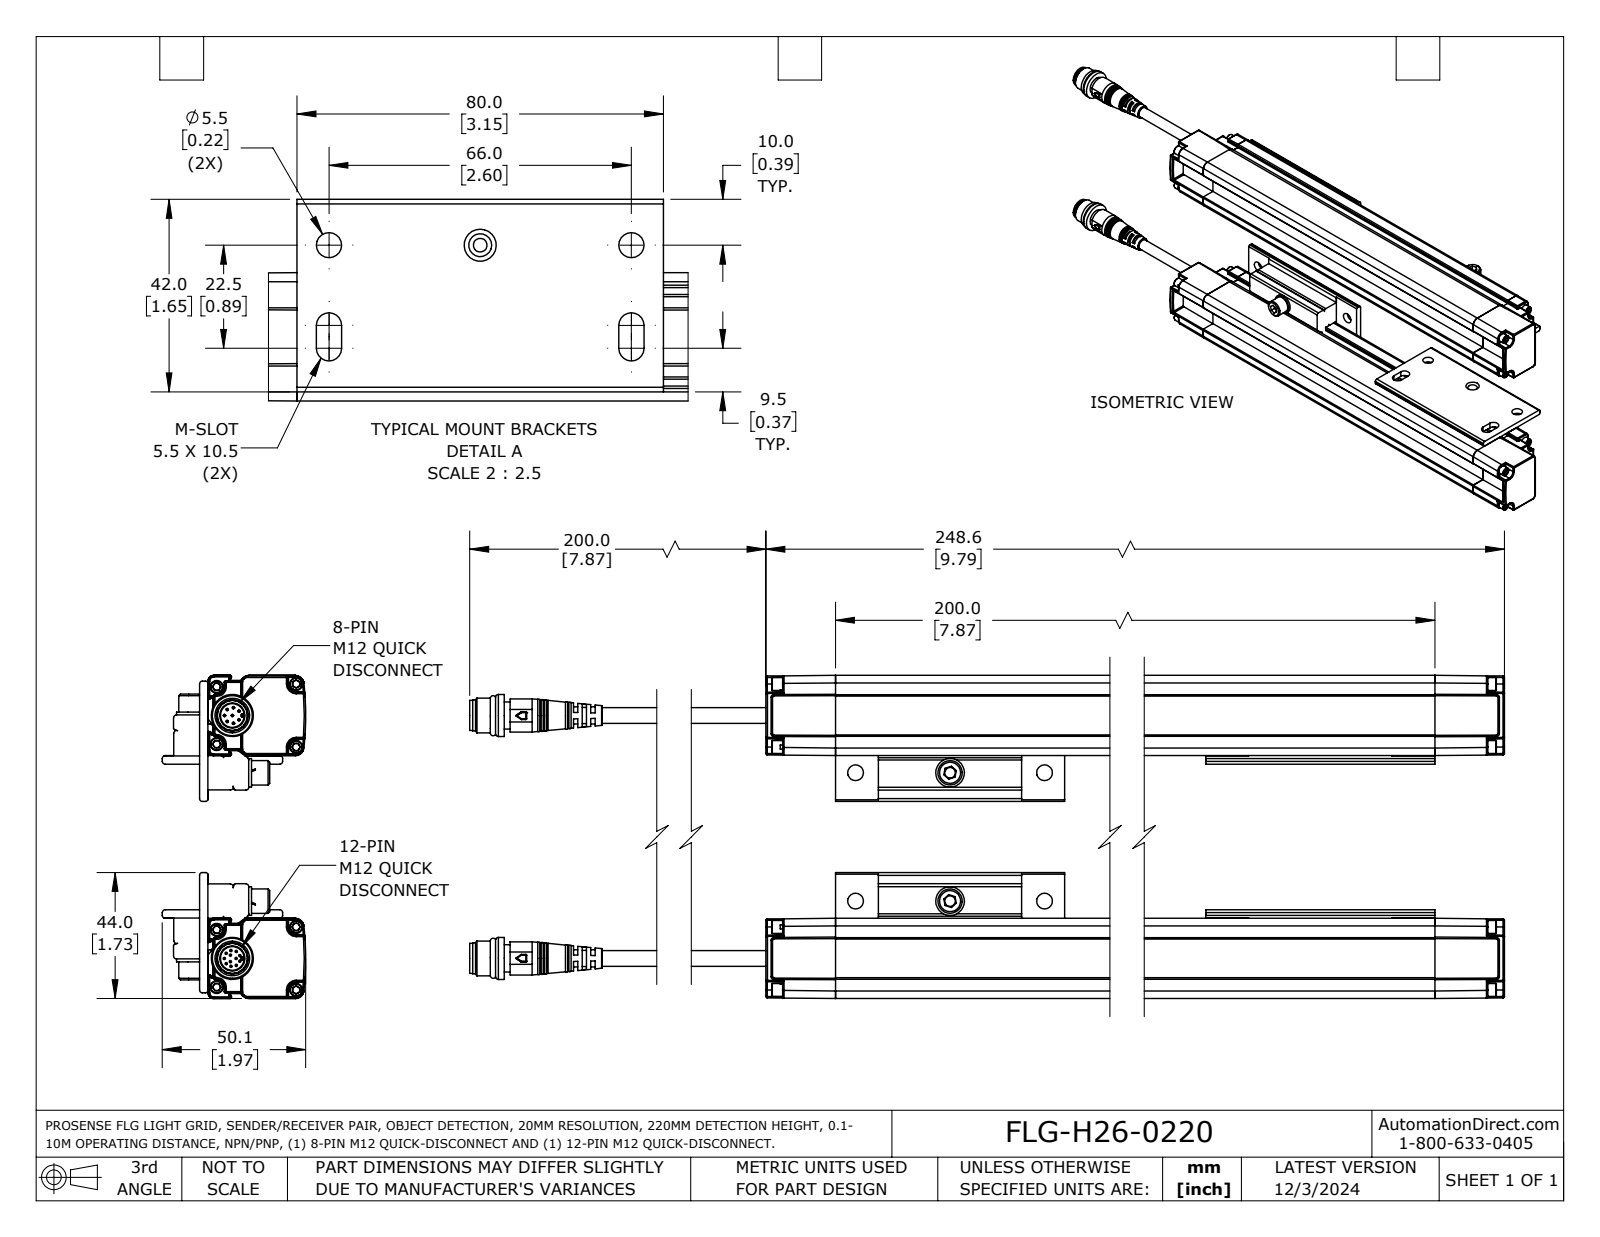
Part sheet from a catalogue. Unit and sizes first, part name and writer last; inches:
Units: inches
Overall size (bounding box): 13.407 × 4.441 × 1.972
Round holes (diameter × count): ⌀0.016 ×16, ⌀0.217 ×6, ⌀0.098 ×4, ⌀0.197 ×3, ⌀0.327 ×2
Round bosses / shafts (diameter × count): ⌀0.031 ×20, ⌀0.177 ×8, ⌀0.118 ×8, ⌀0.217 ×4, ⌀0.059 ×4, ⌀0.394 ×3, ⌀0.335 ×3, ⌀0.146 ×3
Partial cylindrical surfaces — rounded edges, fillets, slot ends (radius × count): R0.02 ×142, R0.039 ×40, R0.01 ×20, R0.008 ×12, R0.012 ×12, R0.108 ×12, R0.1 ×6, R0.049 ×4
Main face-to-face distances: 3.339, 0.118, 1.102, 0.071, 1.041, 0.189, 2.236, 1.22, 3.22, 2.118
Hole centre spacings: 0.108, 1.299, 0.163, 0.979, 2.191, 0.215, 1.764, 2.598
Volume: 27.93 in³ · Surface area: 225.7 in²
Bodies: 10 solids, 1668 faces (816 planar, 456 cylindrical, 396 other)
Part name (STEP PRODUCT): FLG-H26-0220
STEP written by: SolidWorks 2023 (AUTOMOTIVE_DESIGN)
